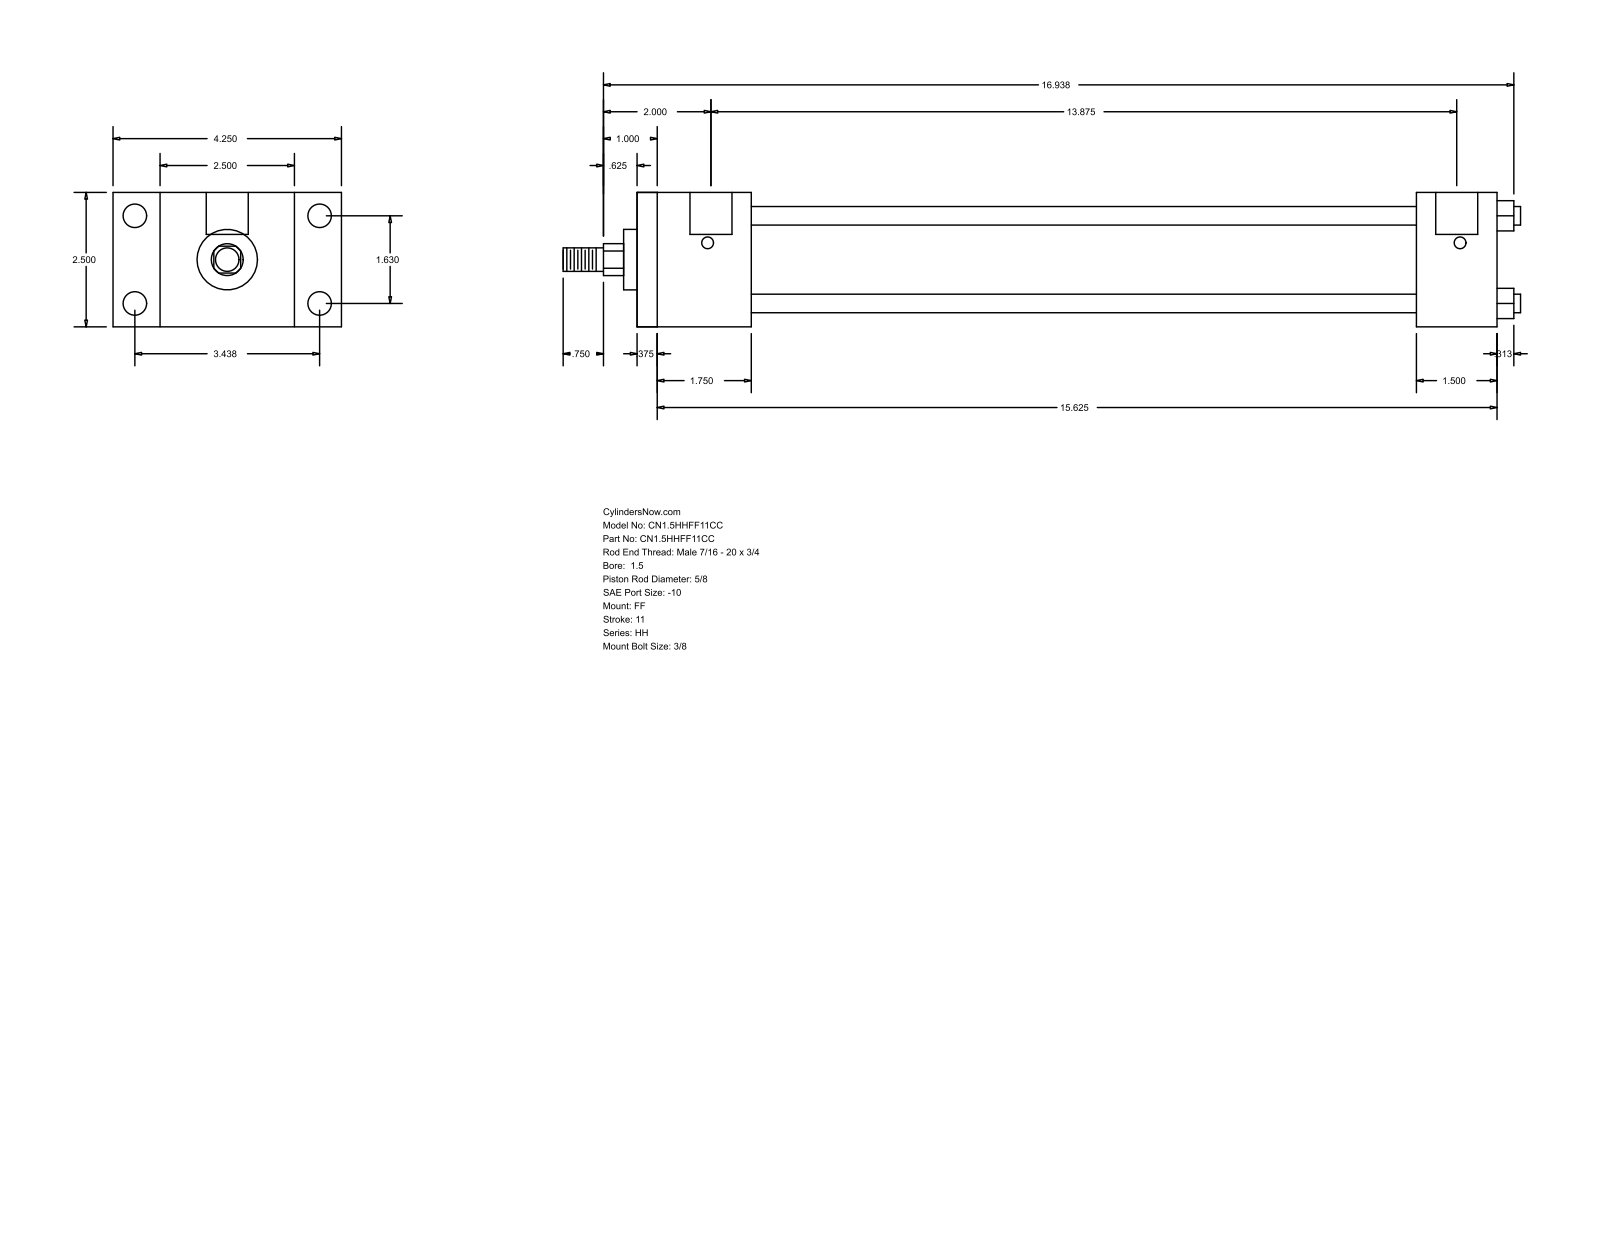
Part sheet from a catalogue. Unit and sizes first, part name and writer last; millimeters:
Units: millimetres
Overall size (bounding box): 452.44 × 107.95 × 63.5
Round holes (diameter × count): ⌀5.56 ×4, ⌀11.13 ×4, ⌀19.84 ×2
Round bosses / shafts (diameter × count): ⌀8.76 ×4, ⌀44.45 ×1, ⌀28.57 ×1, ⌀15.88 ×1, ⌀11.11 ×1
Partial cylindrical surfaces — rounded edges, fillets, slot ends (radius × count): R7.54 ×1
Main face-to-face distances: 63.5, 406.39, 9.52, 396.87, 44.45, 53.97, 352.42, 368.3, 358.78, 314.33
Hole centre spacings: 41.4, 87.32, 96.64, 355.6, 1.58, 1.59, 352.43, 354.01
Bodies: 0 solids, 92 faces (64 planar, 28 cylindrical, 0 other)
Part name (STEP PRODUCT): HH_FF__0150_0.625
STEP written by: GSSL Pune (CONFIG_CONTROL_DESIGN)
